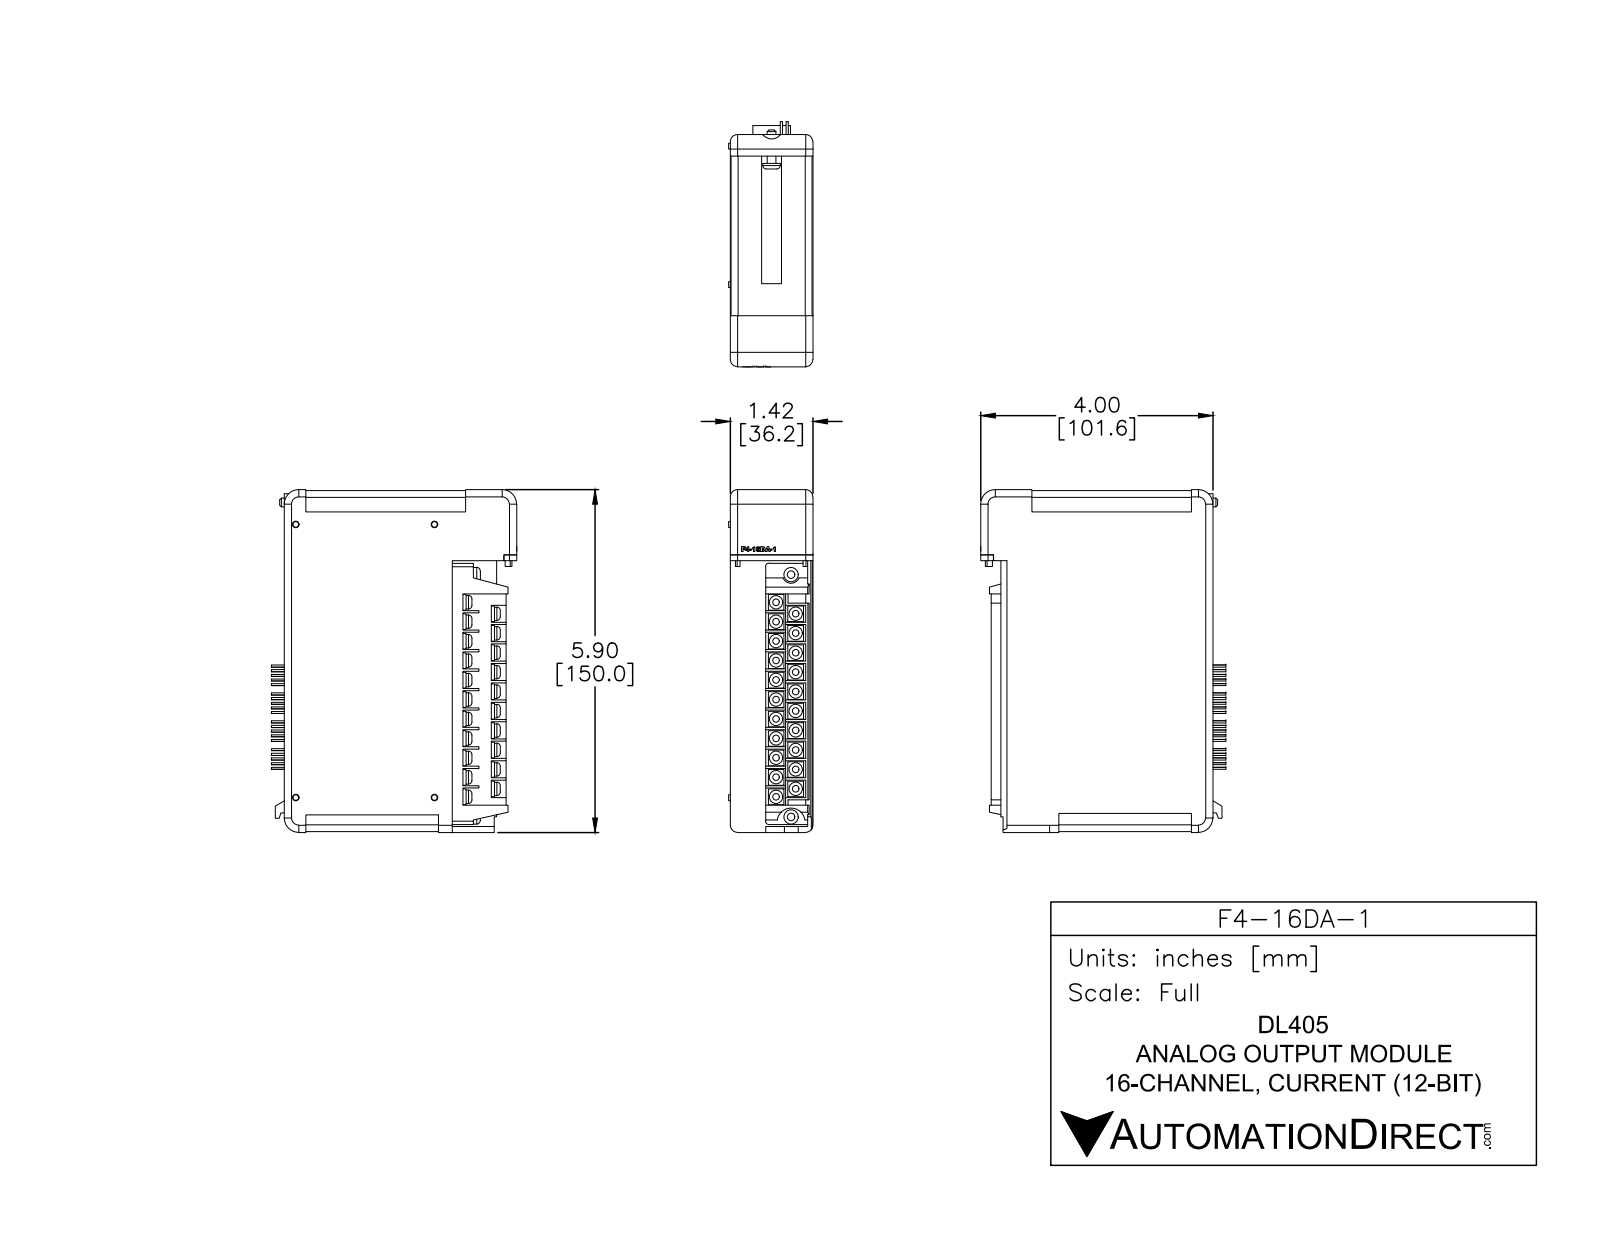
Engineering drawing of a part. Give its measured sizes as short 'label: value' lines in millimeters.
name: F4-16DA-1
written by: SolidWorks 2014 (AUTOMOTIVE_DESIGN)
unit: mm
bodies: 6 solids, 891 faces (561 planar, 246 cylindrical, 84 other)
size: 150 × 107.3 × 37
volume: 452 300 mm³; area: 58 370 mm²
bosses: 21× ⌀5.8, 20× ⌀0.9, 20× ⌀0.9, 2× ⌀6.4, 1× ⌀7.6, 1× ⌀3.8
rounds: 82× R0.4, 8× R3.2, 4× R3, 3× R6.4, 2× R0.8, 2× R1.5, 1× R3.8, 1× R3.8
face distances: 36.2, 0.4, 73.4, 149.2, 35.8, 11.9, 24.3, 149.6, 30.7, 8.8
